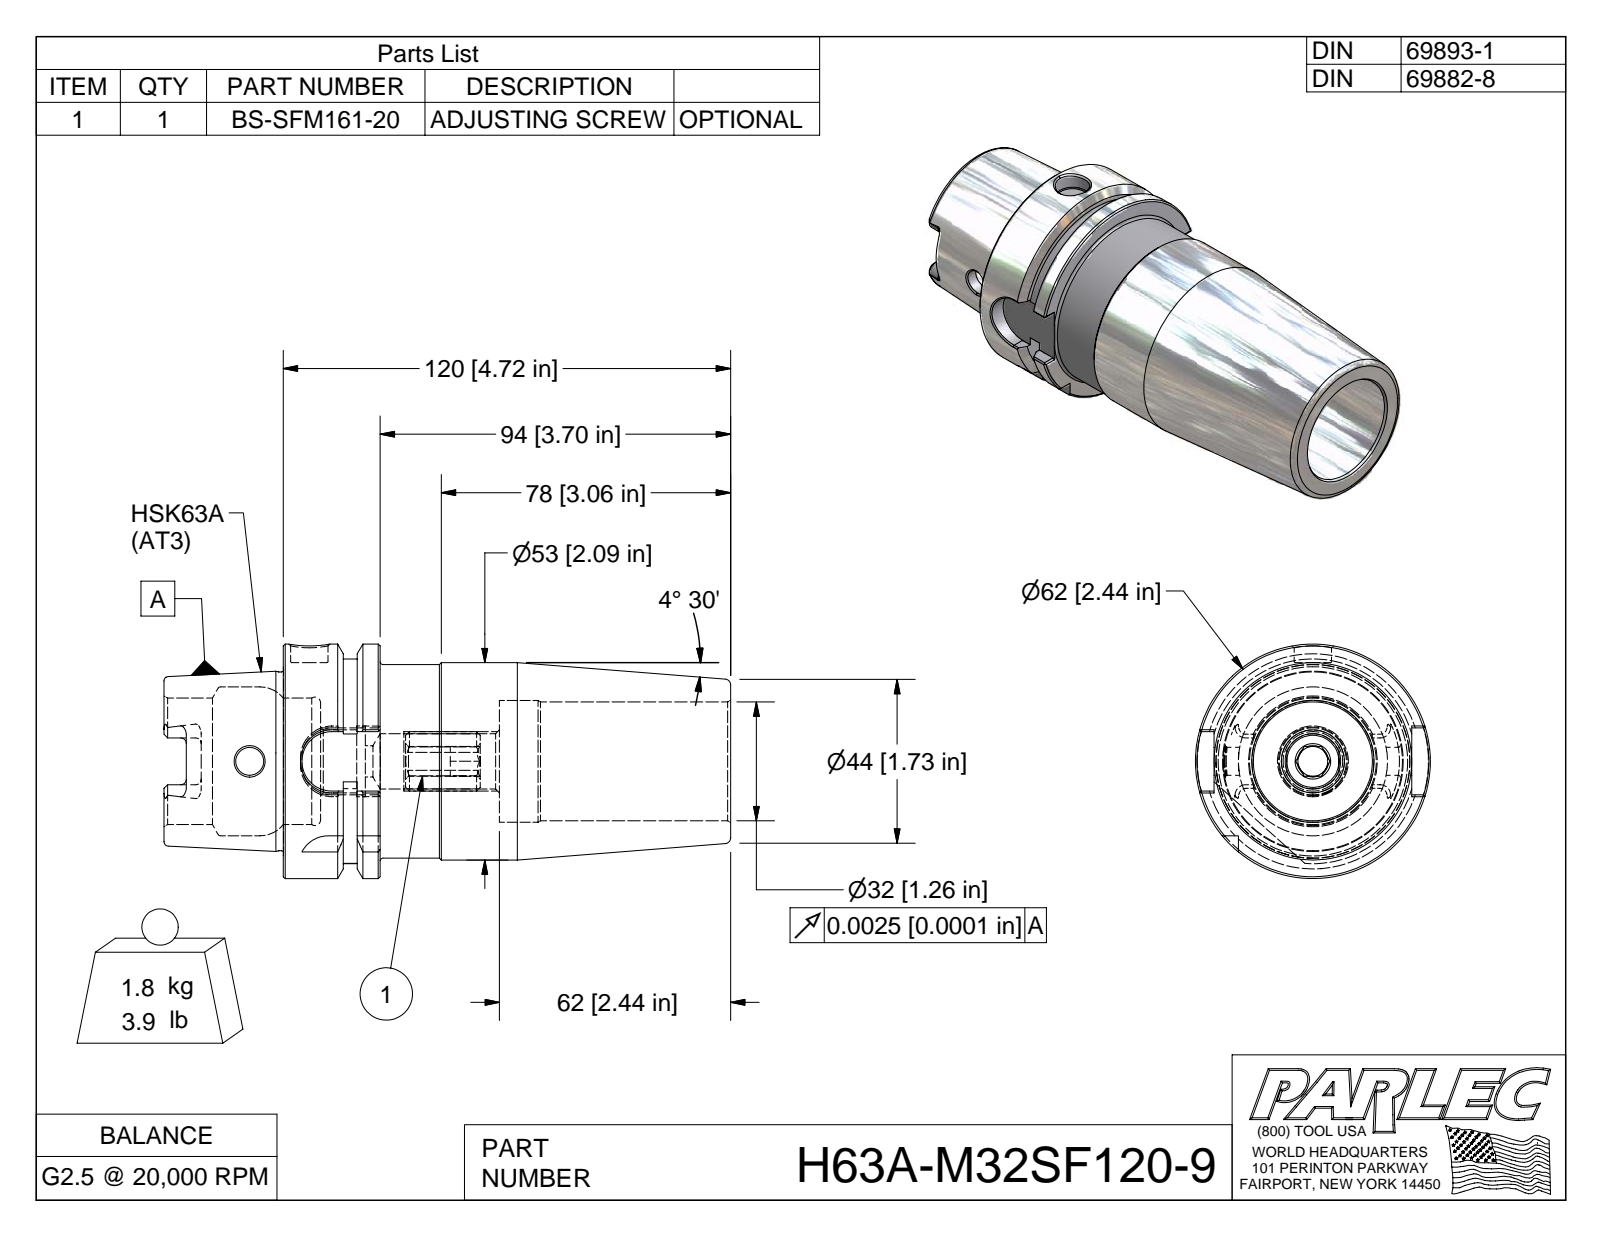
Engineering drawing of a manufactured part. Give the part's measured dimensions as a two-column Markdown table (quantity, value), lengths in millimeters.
| quantity | value |
| --- | --- |
| part name | H63A-M32SF120-9; H63A-M32SF120-9-1; BS-SFM161-20 |
| STEP written by | Autodesk Inventor 2009 (AUTOMOTIVE_DESIGN) |
| units | millimeters |
| bodies | 2 solids, 167 faces (65 planar, 37 cylindrical, 65 other) |
| overall size | 152 × 63 × 63 |
| volume | 213 700 mm³ |
| surface area | 46 060 mm² |
| round holes (diameter × count) | 7.5 × 1, 10 × 1, 16.9 × 1, 19 × 1, 32 × 1, 32.7 × 1, 34 × 1, 40 × 1 |
| round bosses / shafts (diameter × count) | 63 × 1, 53 × 1, 52 × 1, 48 × 1 |
| partial cylindrical surfaces (radius × count) | 1.5 × 6, 8 × 5, 2.9 × 4, 27.5 × 1 |
| main face-to-face distances | 32, 58, 26, 6.1, 9.9, 48, 10, 16, 120, 110 |
